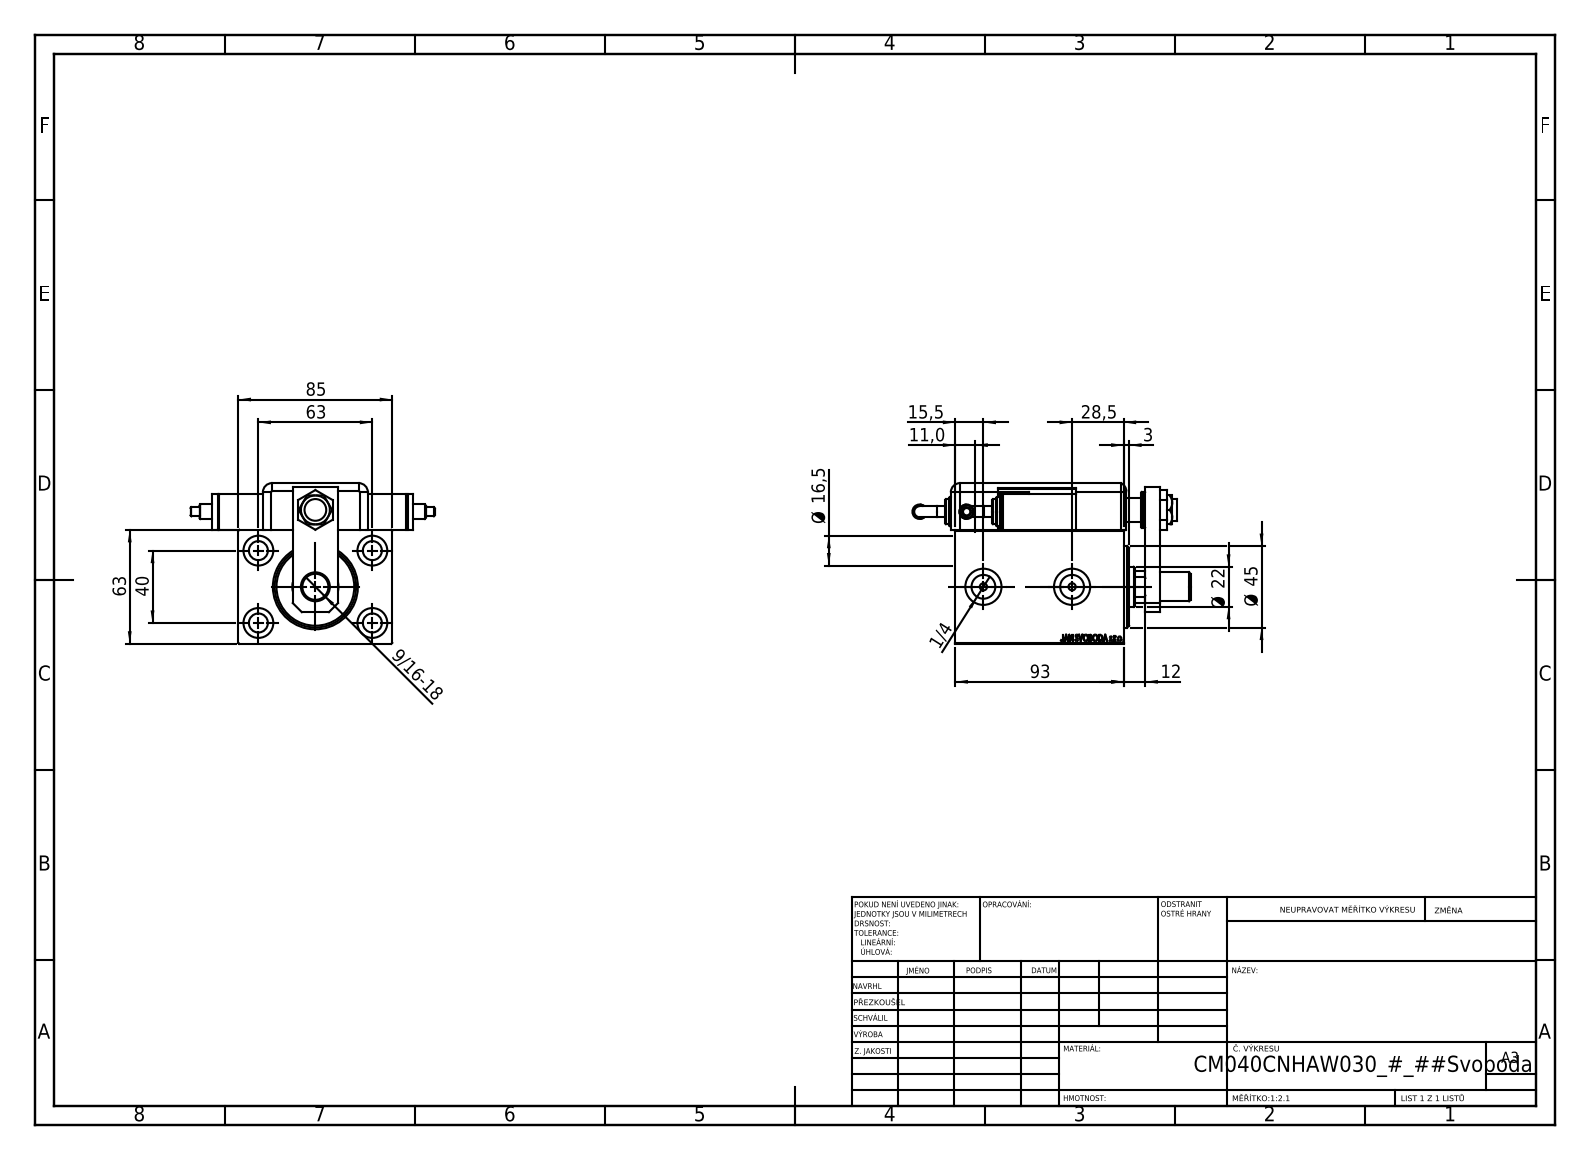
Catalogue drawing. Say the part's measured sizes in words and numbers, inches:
The part is named "NUT_D13; NUT_D19; KRYT; ZARAZKA_Q (+8 more)". Its 3-D file was written by "SolidWorks 2019 (CONFIG_CONTROL_DESIGN)". It is 14 solids with 1288 faces: 622 planar, 127 cylindrical and 539 other. Overall it measures 6.054 by 5.315 by 3.496 inches. Its volume is 34.9 cubic inches and its surface area 209 square inches. Round holes: 4 of diameter 0.157, 4 of diameter 0.413, 4 of diameter 0.65, 2 of diameter 0.315, 2 of diameter 0.518, 2 of diameter 0.551, 2 of diameter 0.787, 1 of diameter 0.472, 1 of diameter 0.492, 1 of diameter 0.512, 1 of diameter 0.866, 1 of diameter 1.004. Round bosses or shafts: 3 of diameter 0.787, 3 of diameter 0.63, 3 of diameter 0.551, 2 of diameter 0.315, 2 of diameter 0.236, 2 of diameter 0.198. Partial cylindrical surfaces (rounded edges, fillets, slot ends): 9 of radius 0.197, 1 of radius 0.394, 1 of radius 0.413. The main face-to-face distances are 0.118, 2.48, 0.531, 3.346, 0.472, 3.661, 0.787, 3.268, 1.016, 3.496. The hole center spacings are 1.469, 1.448, 1.491, 1.524, 1.575, 2.48, 2.756, 2.938.
